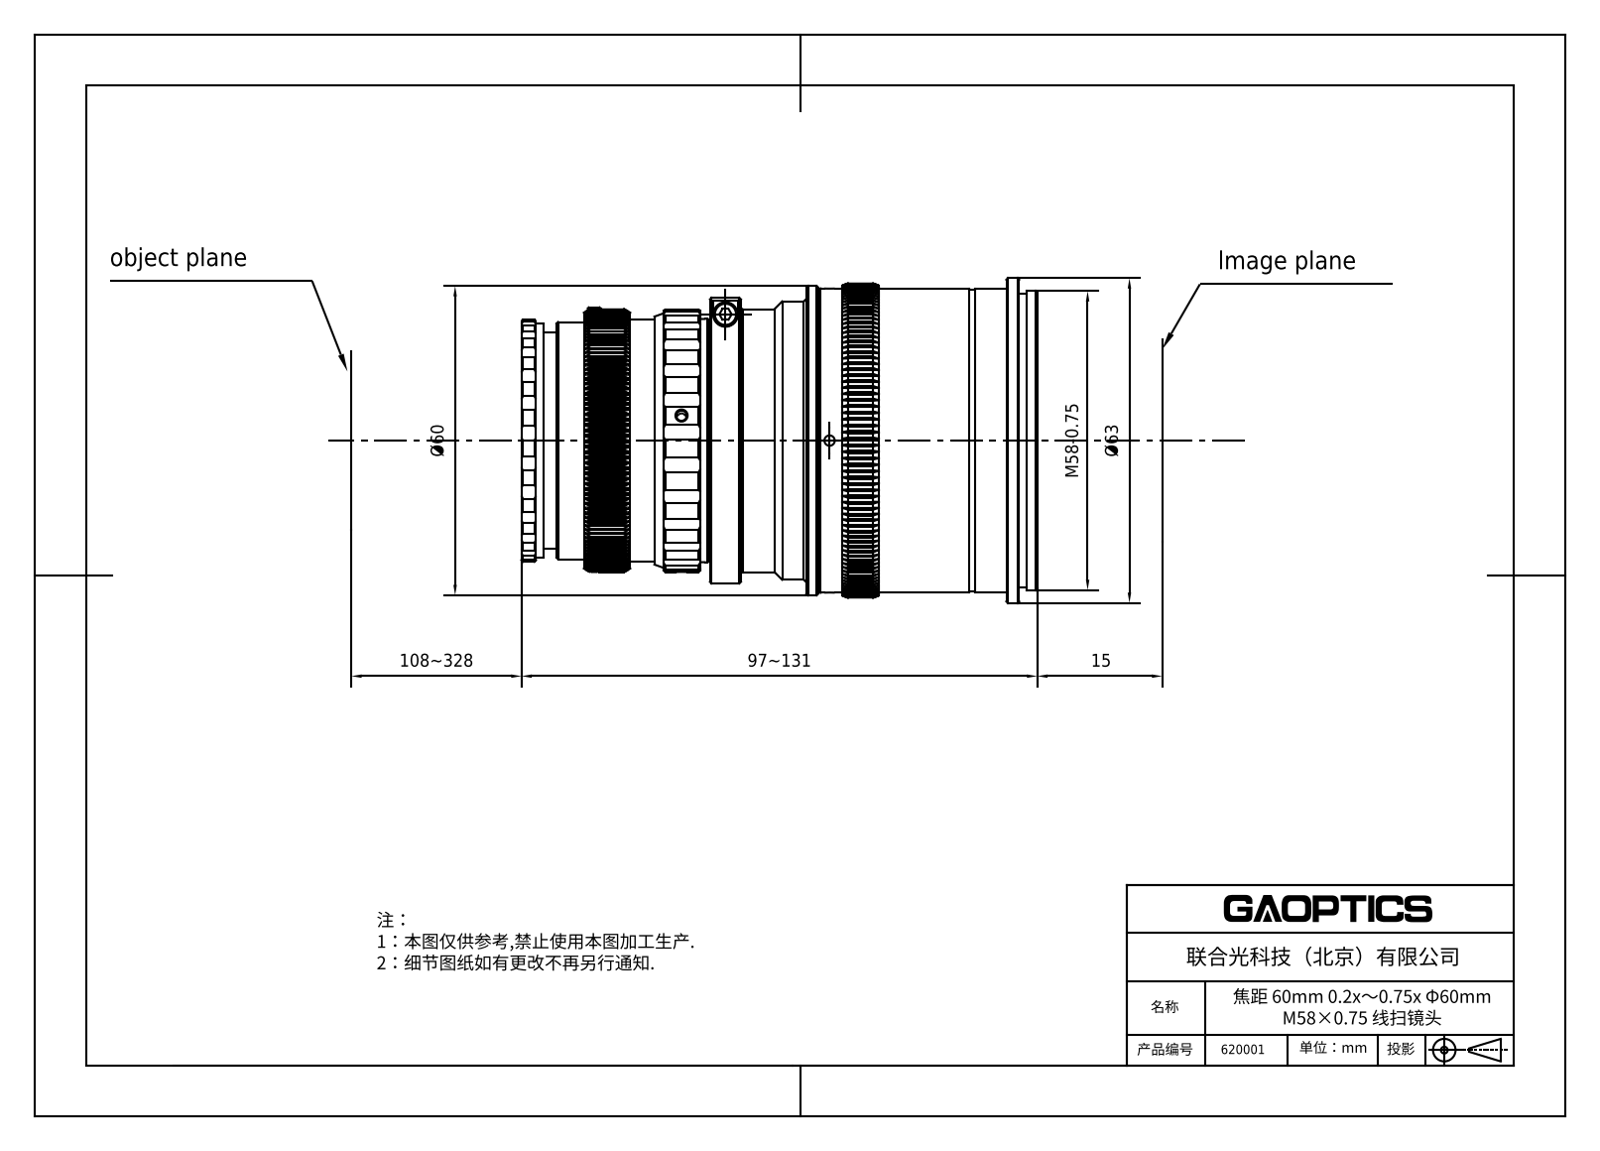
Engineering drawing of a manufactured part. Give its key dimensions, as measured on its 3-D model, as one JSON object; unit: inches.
{"part_name": "620001", "step_written_by": "SolidWorks 2016 (CONFIG_CONTROL_DESIGN)", "units": "inches", "bodies": {"solids": 18, "faces": 2368, "planar": 847, "cylindrical": 913, "other": 608}, "overall_size": [3.941, 2.48, 2.48], "volume_in3": 7.001, "surface_area_in2": 128.7, "round_holes": [[0.079, 7], [0.055, 1], [0.059, 1], [0.102, 1], [0.433, 1], [0.637, 1], [0.748, 1], [0.835, 1], [0.929, 1], [0.945, 1], [0.984, 1], [1.008, 1]], "round_bosses_or_shafts": [[0.098, 2], [2.48, 1], [2.362, 1], [2.323, 1], [2.299, 1], [2.283, 1], [2.246, 1], [2.181, 1]], "partial_cylinders_radius": [[0.008, 150], [0.098, 50], [0.039, 7], [0.197, 4], [0.03, 1], [0.069, 1], [0.094, 1], [0.157, 1]], "face_to_face_distances": [0.236, 0.098, 1.004, 0.177, 1.113, 0.161, 0.768, 0.492, 0.728, 1.496], "hole_center_spacings": [0.157, 0.305, 0.463, 0.667, 0.669, 0.825, 0.974, 1.13]}
